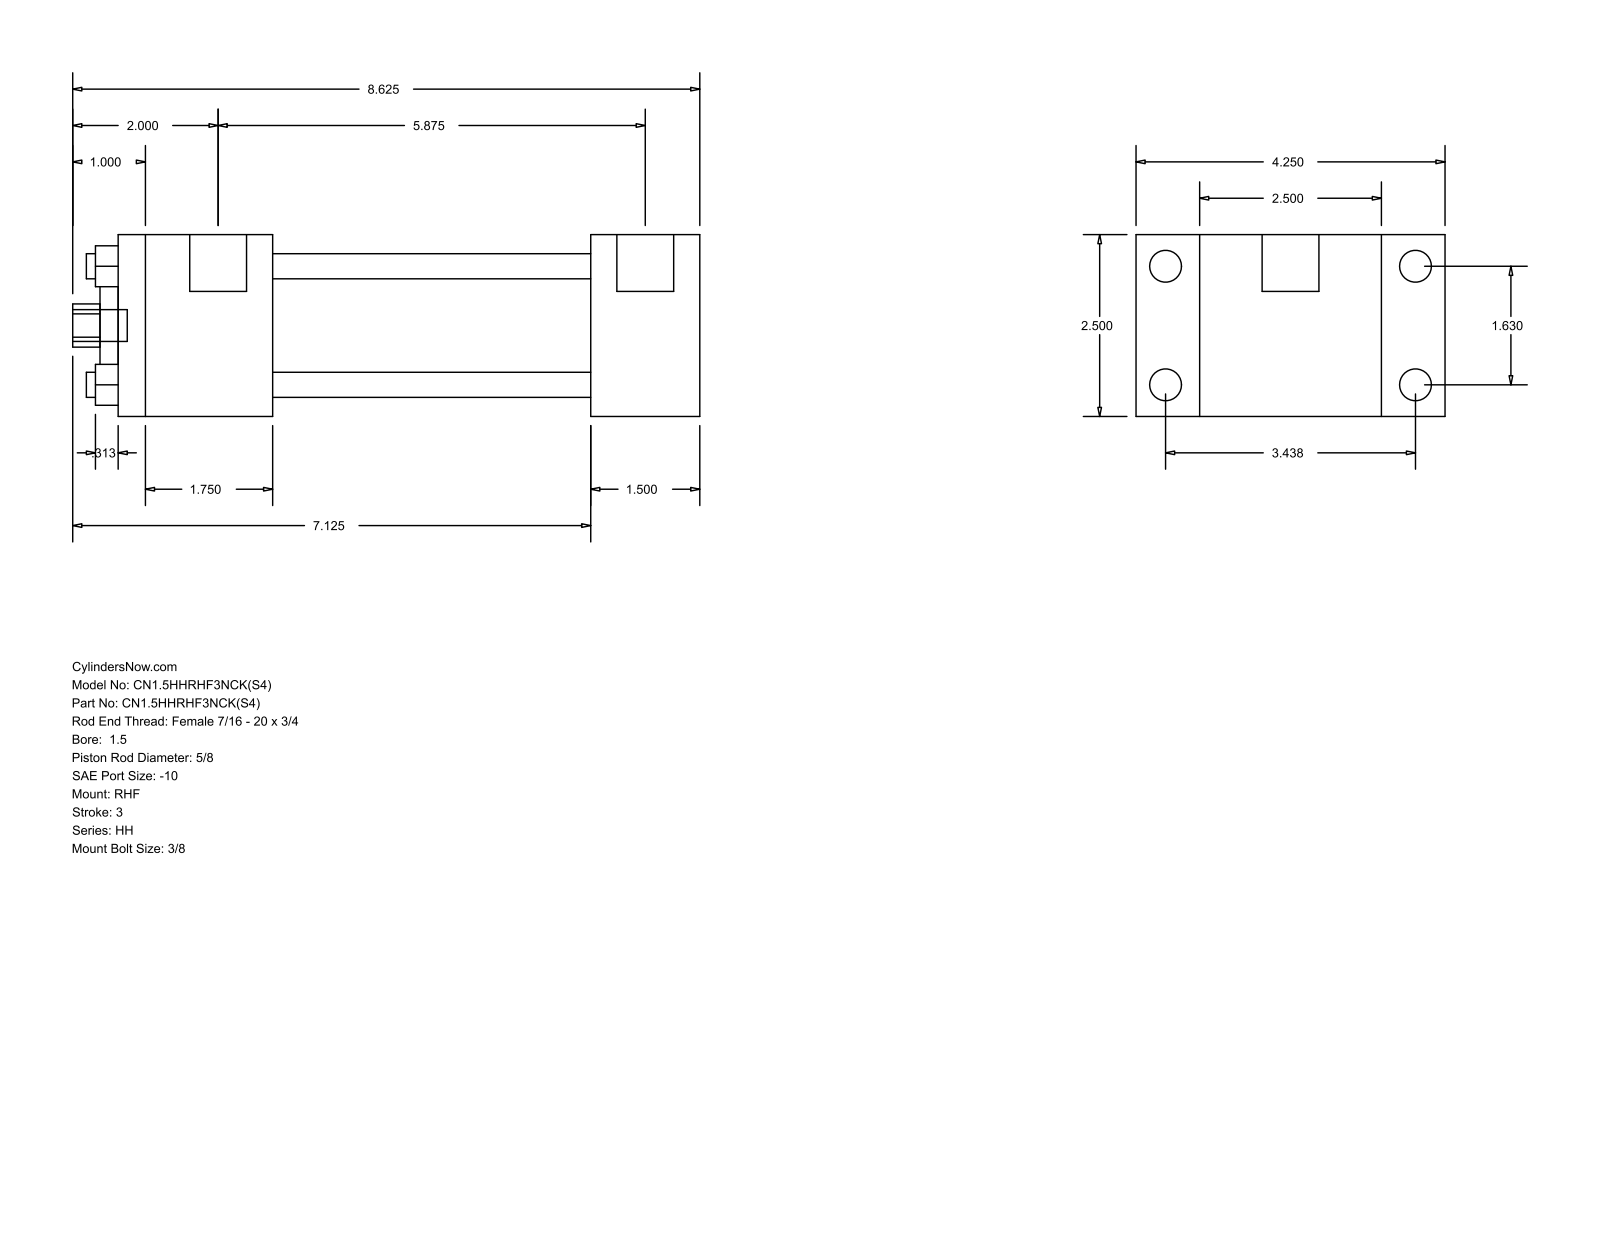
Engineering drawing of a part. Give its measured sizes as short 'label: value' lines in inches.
name: HH_RHF__0150_0.625
written by: GSSL Pune (CONFIG_CONTROL_DESIGN)
unit: in
bodies: 0 solids, 88 faces (60 planar, 28 cylindrical, 0 other)
size: 8.625 × 4.25 × 2.5
holes: 4× ⌀0.345, 1× ⌀0.625, 1× ⌀1.125, 1× ⌀1.75
bosses: 4× ⌀0.438, 4× ⌀0.219, 2× ⌀0.781, 1× ⌀0.437
rounds: 1× R0.297
face distances: 2.5, 1.5, 0.875, 3.375, 6.5, 8, 4.25, 2.125, 4.375, 5.875
hole spacings: 1.152, 1.63, 2.305
